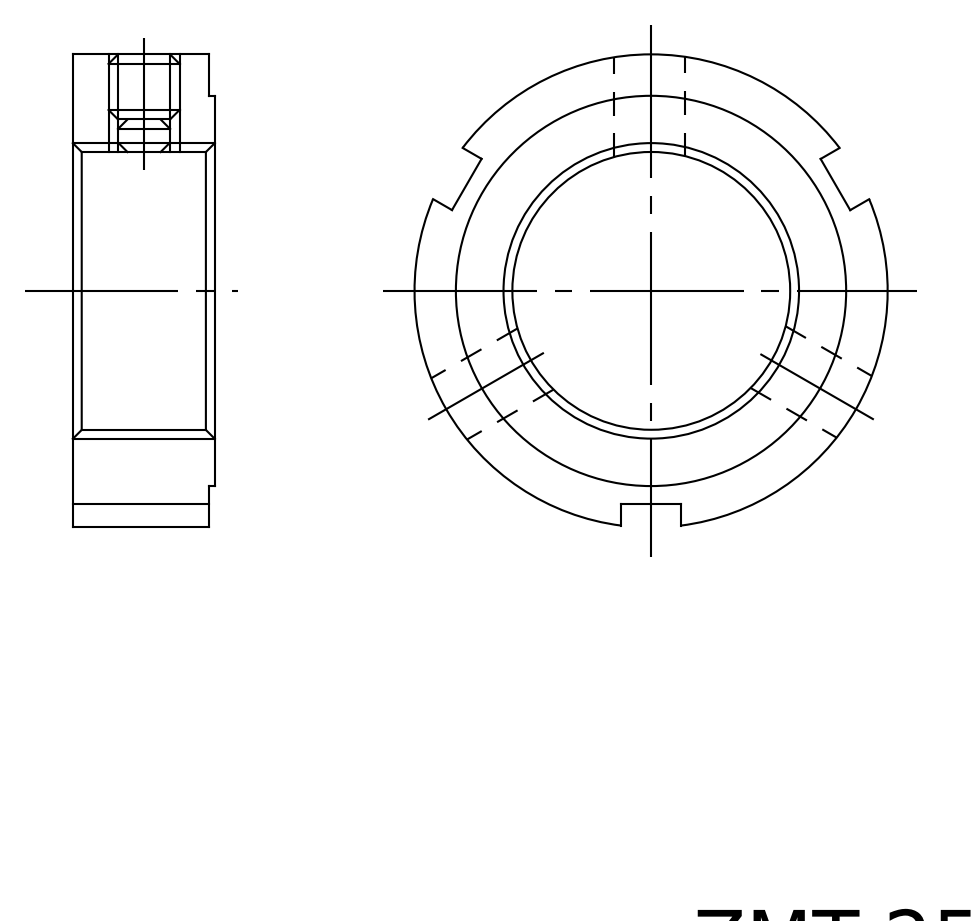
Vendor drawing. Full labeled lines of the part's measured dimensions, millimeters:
Part name (STEP PRODUCT): FKD ZMT 25A
STEP written by: Autodesk Inventor 2011 (AUTOMOTIVE_DESIGN)
Units: millimetres
Bodies: 1 solid, 20 faces (12 planar, 8 cylindrical, 0 other)
Overall size (bounding box): 40 × 39.84 × 12
Volume: 8 224 mm³ · Surface area: 4 275 mm²
Round holes (diameter × count): ⌀4.92 ×3, ⌀25 ×1
Round bosses / shafts (diameter × count): ⌀40 ×1, ⌀33 ×1
Main face-to-face distances: 11.5, 0.5, 12, 5
